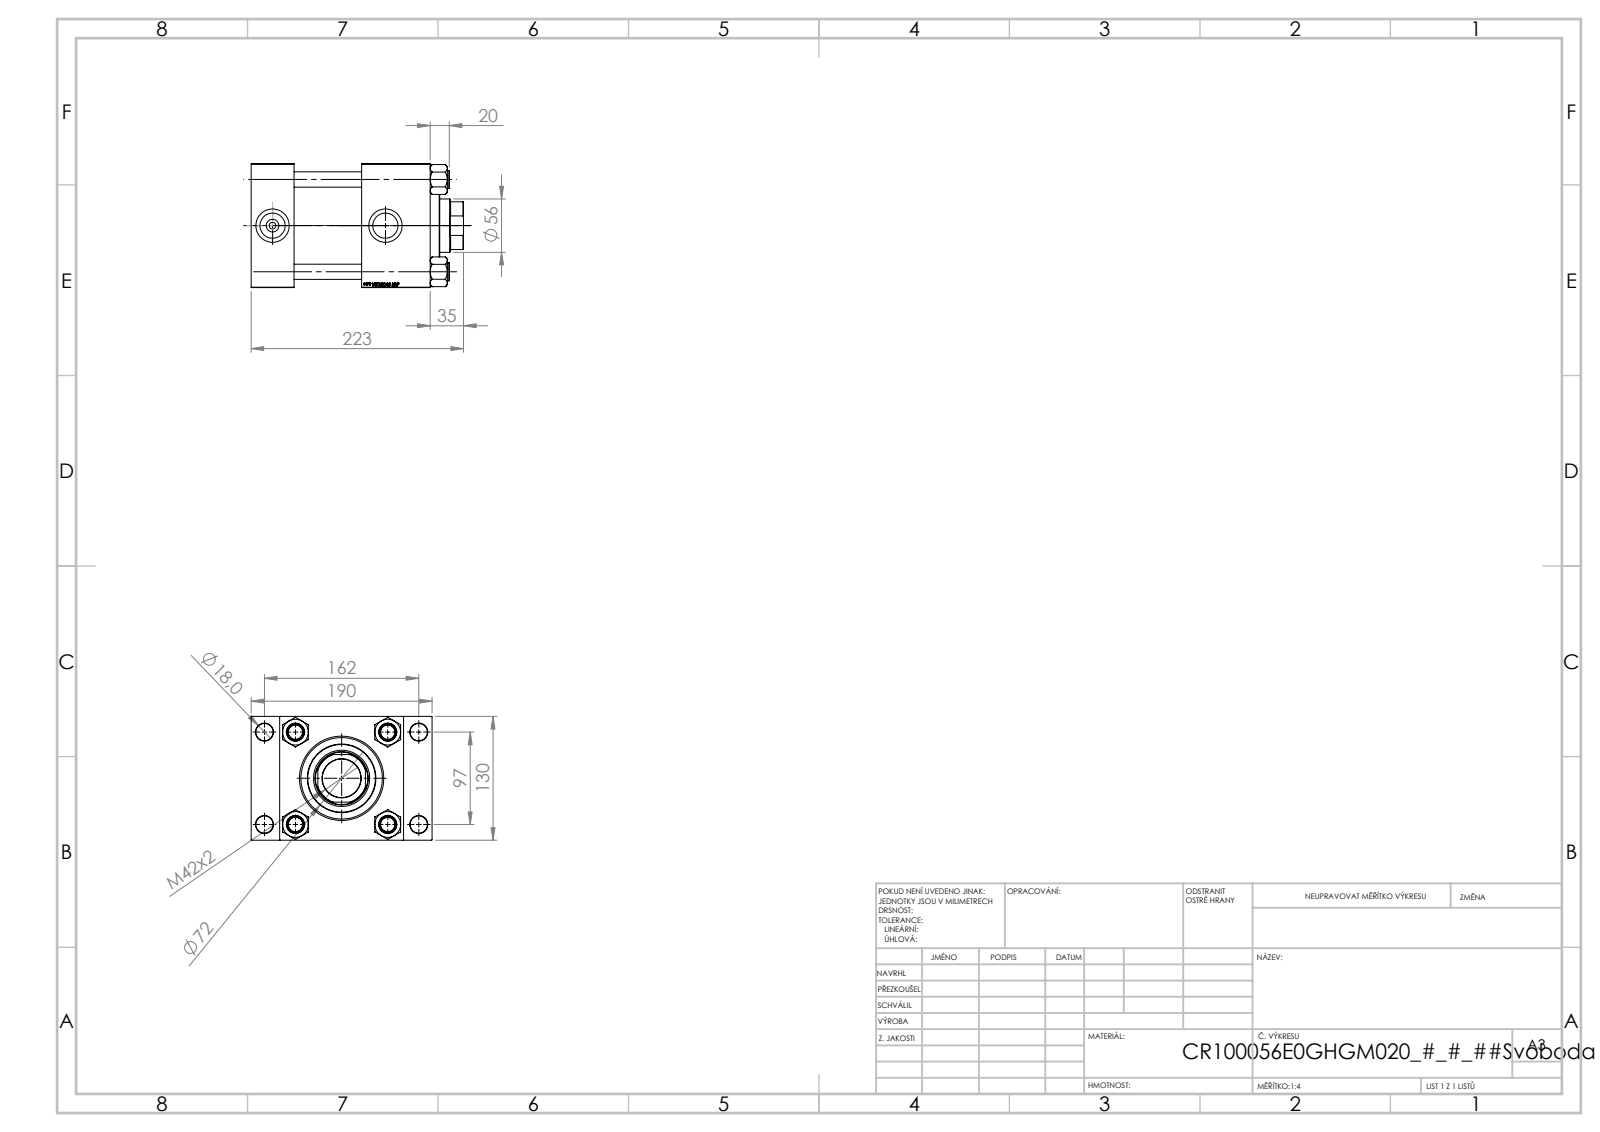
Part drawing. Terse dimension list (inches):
name: NUT_M5_E; V215CR_VCP_E; V215_VC_A; V215CR_TYCINKA_E (+1 more)
written by: SolidWorks 2019 (CONFIG_CONTROL_DESIGN)
unit: in
bodies: 11 solids, 1184 faces (546 planar, 86 cylindrical, 552 other)
size: 8.78 × 7.48 × 5.118
volume: 170.6 in³; area: 584.5 in²
holes: 4× ⌀0.63, 4× ⌀0.709, 2× ⌀0.276, 2× ⌀1.041, 2× ⌀1.378, 1× ⌀1.594, 1× ⌀2.205, 1× ⌀2.323, 1× ⌀2.992, 1× ⌀3.366, 1× ⌀3.937
bosses: 4× ⌀0.748, 1× ⌀4.173, 1× ⌀2.835
rounds: 1× R1.063
face distances: 5.118, 1.772, 7.402, 5.63, 1.181, 6.299, 4.567, 2.795, 2.835, 0.787
hole spacings: 1.281, 2.698, 3.717, 3.815, 4.026, 5.096, 6.367, 3.819
